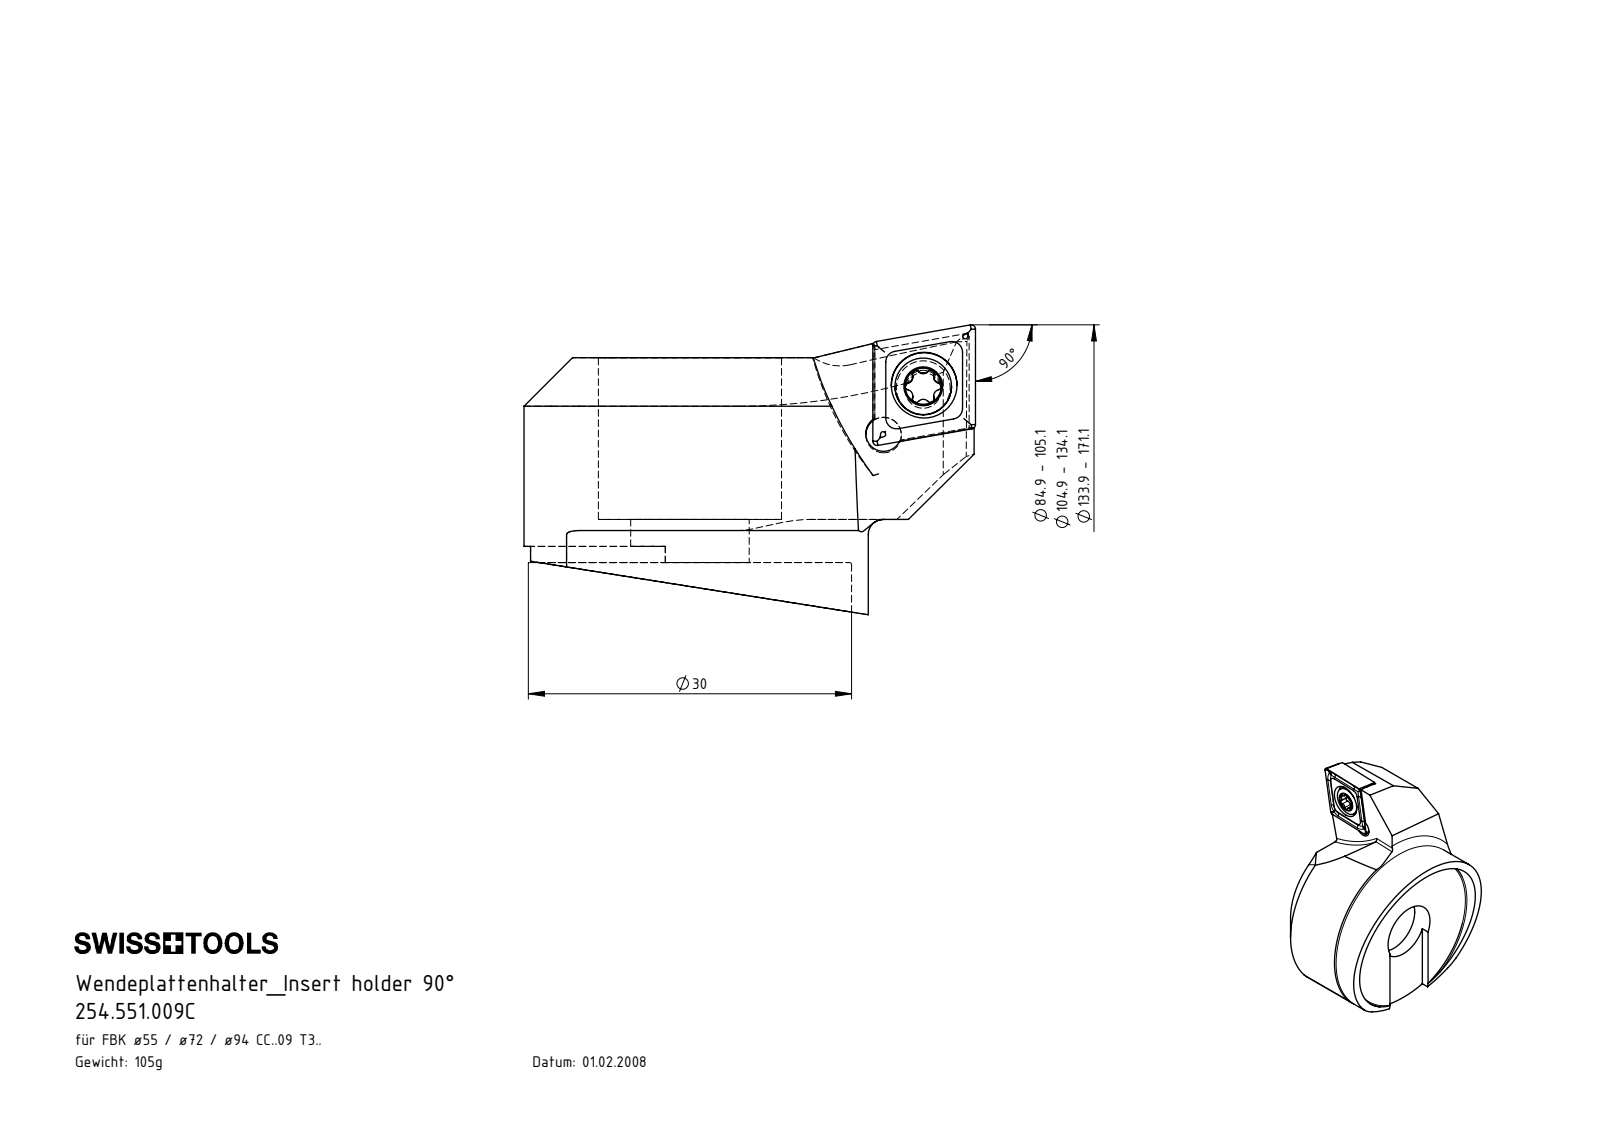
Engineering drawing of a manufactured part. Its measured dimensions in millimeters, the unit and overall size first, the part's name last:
Units: millimetres
Overall size (bounding box): 41.9 × 33.2 × 26.89
Round holes (diameter × count): ⌀3.3 ×2, ⌀4.4 ×1, ⌀6.1 ×1, ⌀11 ×1, ⌀17 ×1, ⌀30 ×1
Round bosses / shafts (diameter × count): ⌀5.25 ×1, ⌀4 ×1
Partial cylindrical surfaces — rounded edges, fillets, slot ends (radius × count): R0.34 ×6, R0.59 ×6, R0.5 ×2, R10 ×2, R1.65 ×1, R5 ×1, R16.55 ×1, R16.6 ×1
Main face-to-face distances: 19, 1, 18, 15, 14, 4, 3.77, 17.5, 16.5, 2.5
Hole centre spacings: 5.73, 5.86
Volume: 13 868 mm³ · Surface area: 6 463 mm²
Bodies: 5 solids, 164 faces (50 planar, 51 cylindrical, 63 other)
Part name (STEP PRODUCT): CCMT09T304; WCB-ER2.001.009_A; F55-WCB.001.022_D_fertigbearbeitet; 254.551.009C
STEP written by: SolidWorks 2017 (CONFIG_CONTROL_DESIGN)
